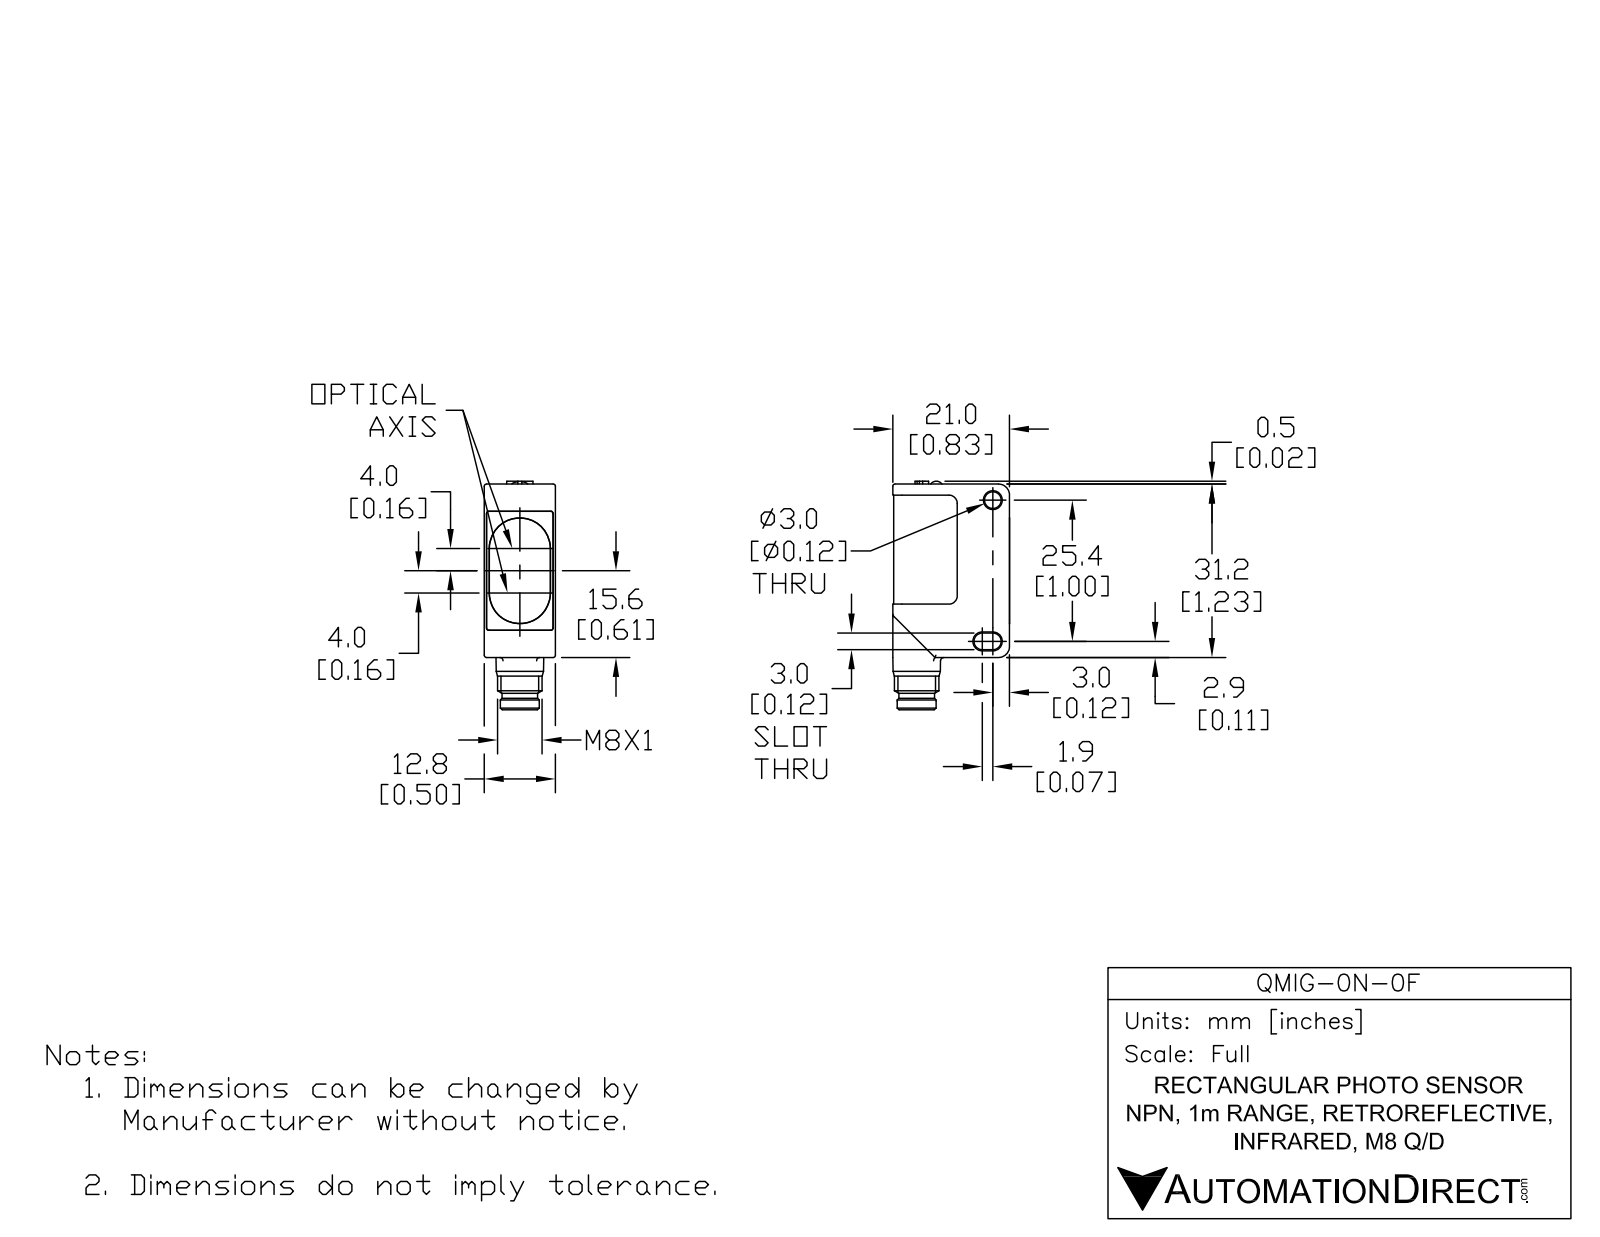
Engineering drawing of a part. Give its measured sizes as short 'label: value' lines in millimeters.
name: QMIG-0N-0F
written by: SolidWorks 2017 (AUTOMOTIVE_DESIGN)
unit: mm
bodies: 7 solids, 272 faces (125 planar, 100 cylindrical, 47 other)
size: 41.1 × 21 × 12.8
volume: 7 770 mm³; area: 4 999 mm²
holes: 3× ⌀3, 1× ⌀5.8
bosses: 4× ⌀1, 2× ⌀3.5, 1× ⌀8, 1× ⌀7, 1× ⌀6.4
rounds: 10× R0.4, 9× R0.5, 6× R1.5, 4× R0.6, 4× R1, 2× R0.2, 2× R1.1, 2× R1.7
face distances: 12.6, 0.5, 12.8, 2.8, 0.4, 12.5, 12.4, 12.2, 1.5, 18.1
hole spacings: 1, 5.2, 6.2
